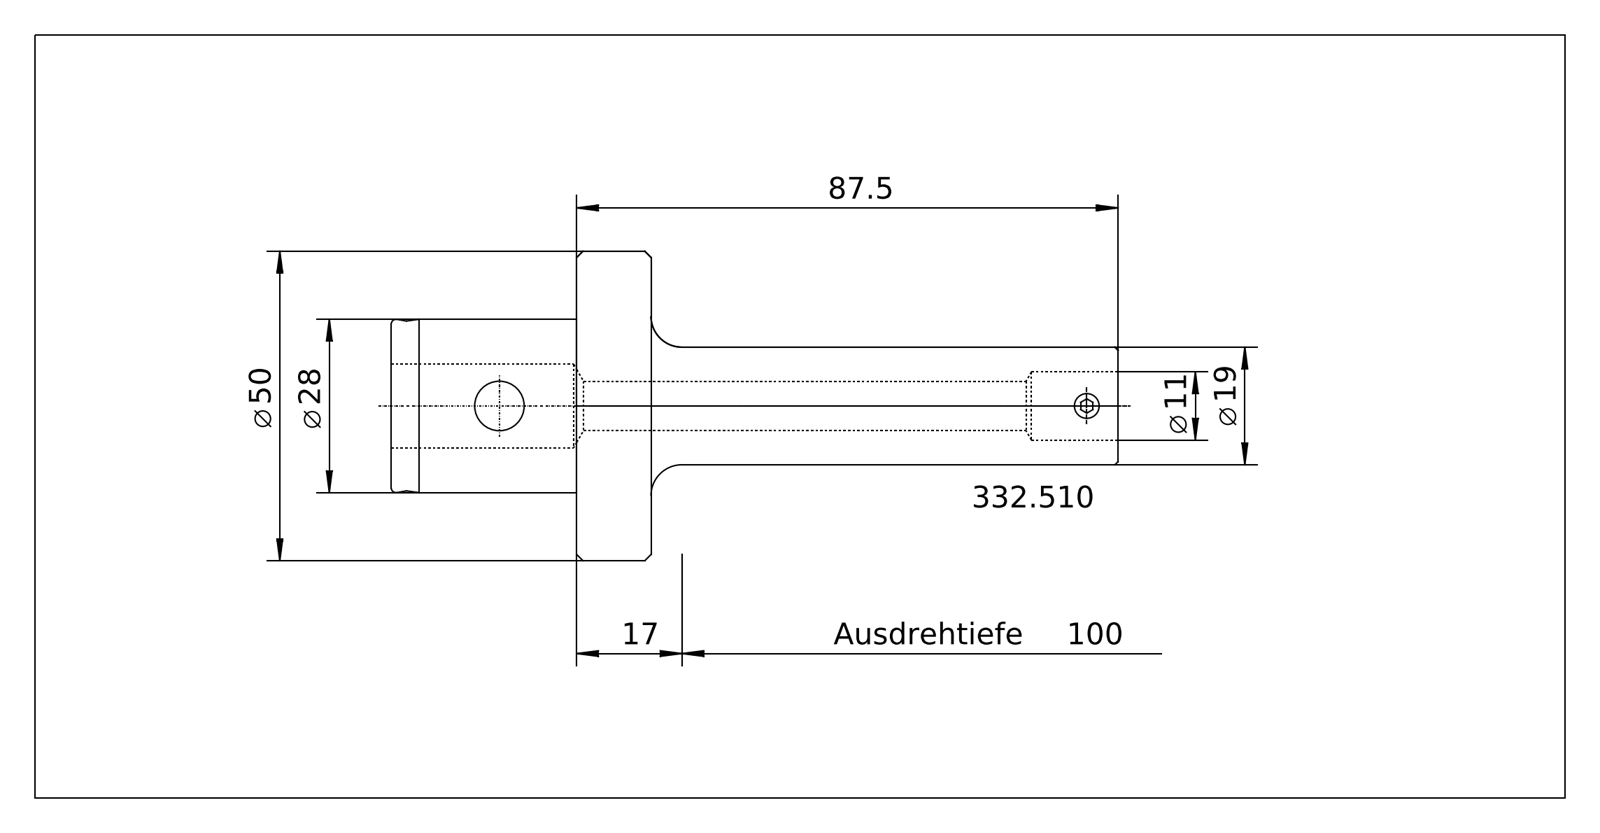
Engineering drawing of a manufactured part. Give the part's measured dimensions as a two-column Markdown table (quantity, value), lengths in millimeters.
| quantity | value |
| --- | --- |
| part name | 332.510 Kaiser CK5 X CK1 X 100B\|332.510 Kaiser CK5 X CK1 X 100B_Standard;NONE; 332.510 Kaiser CK5 X CK1 X 100B\|690.431 Kaiser ETL M4 X 5 CK1_Standard;NONE |
| STEP written by | ACIS (automotive_design) |
| units | millimeters |
| bodies | 2 solids, 110 faces (28 planar, 30 cylindrical, 52 other) |
| overall size | 117.5 × 50 × 50 |
| volume | 53 291 mm³ |
| surface area | 16 589 mm² |
| round holes (diameter × count) | 8 × 2, 3.46 × 1, 4.2 × 1, 4.5 × 1, 11 × 1, 11.5 × 1, 13.5 × 1 |
| round bosses / shafts (diameter × count) | 50 × 1, 28 × 1, 19 × 1, 18.5 × 1, 4 × 1 |
| partial cylindrical surfaces (radius × count) | 1.5 × 2 |
| main face-to-face distances | 11.9, 41.9, 30, 75.6, 87.5, 117.5, 9.34, 5.9, 69.7, 81.6 |
| hole center spacings | 10.5, 94.95 |
